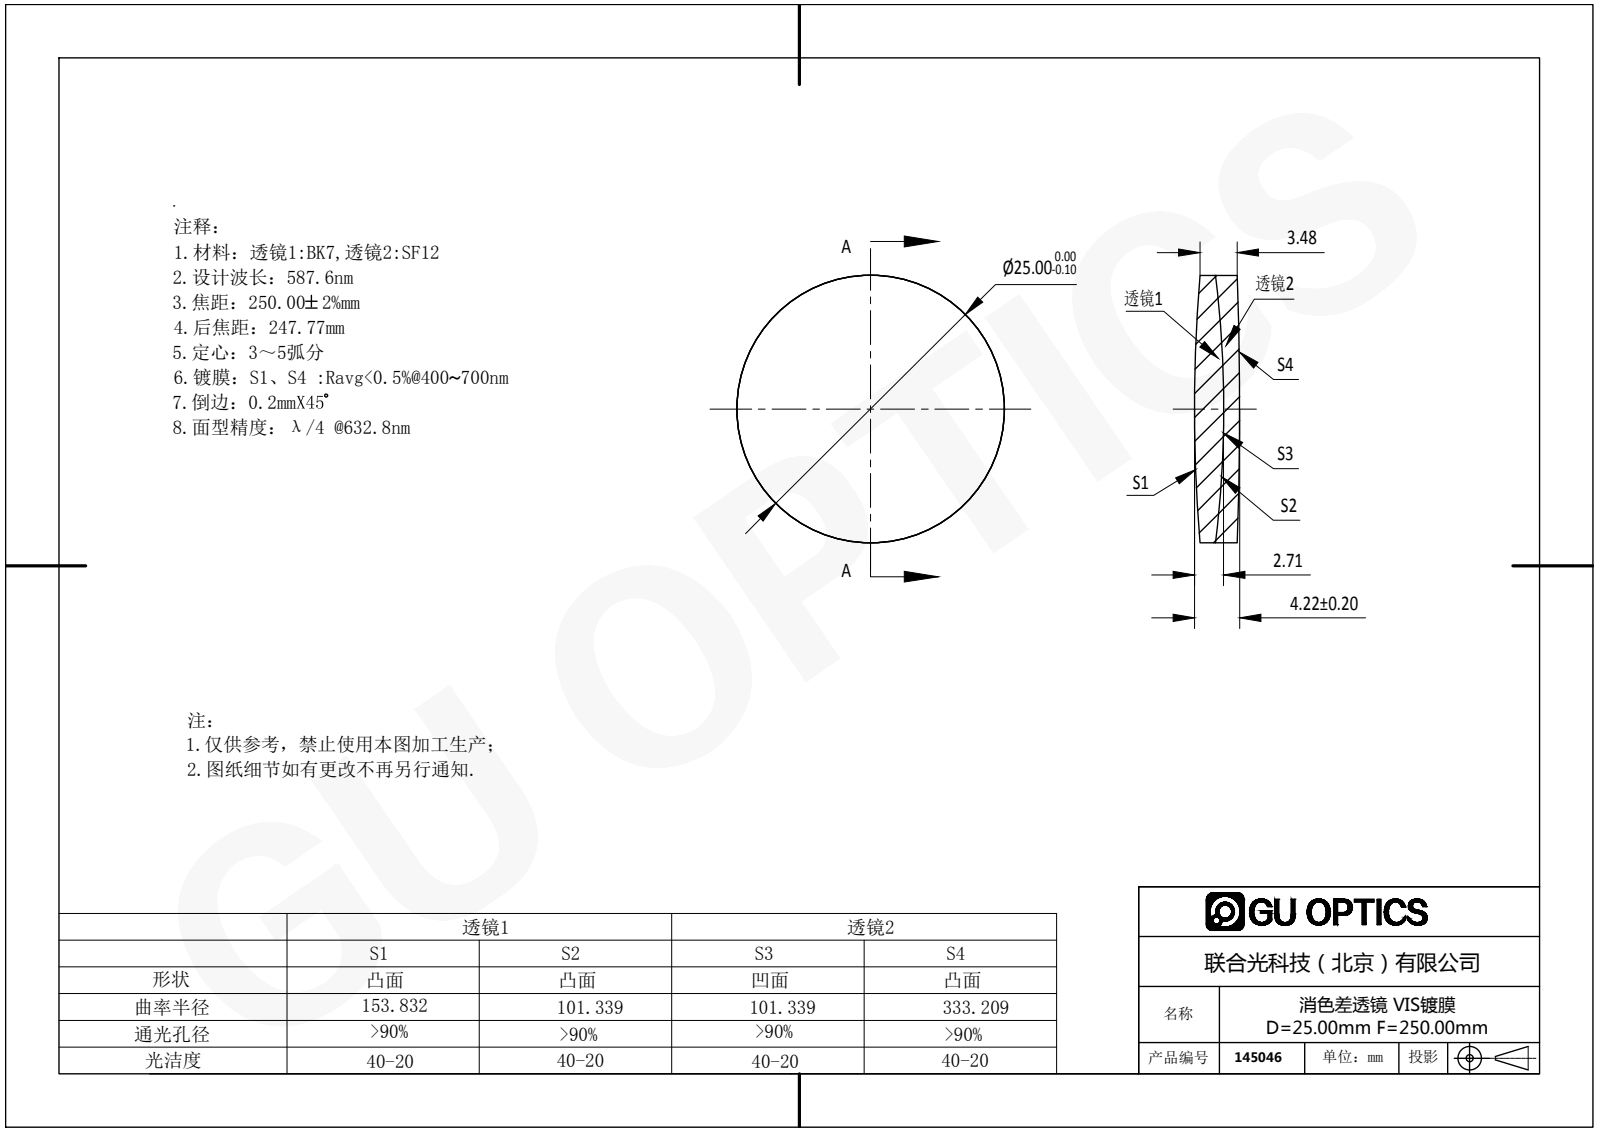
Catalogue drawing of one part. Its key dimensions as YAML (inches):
part_name: "145046"
step_written_by: "SolidWorks 2016 (AUTOMOTIVE_DESIGN)"
units: inches
bodies: {solids: 2, faces: 12, planar: 0, cylindrical: 4, other: 8}
overall_size: [0.984, 0.984, 0.166]
volume: 0.115
surface_area: 3.474
round_bosses_or_shafts:
  - {diameter: 0.984, count: 1}
